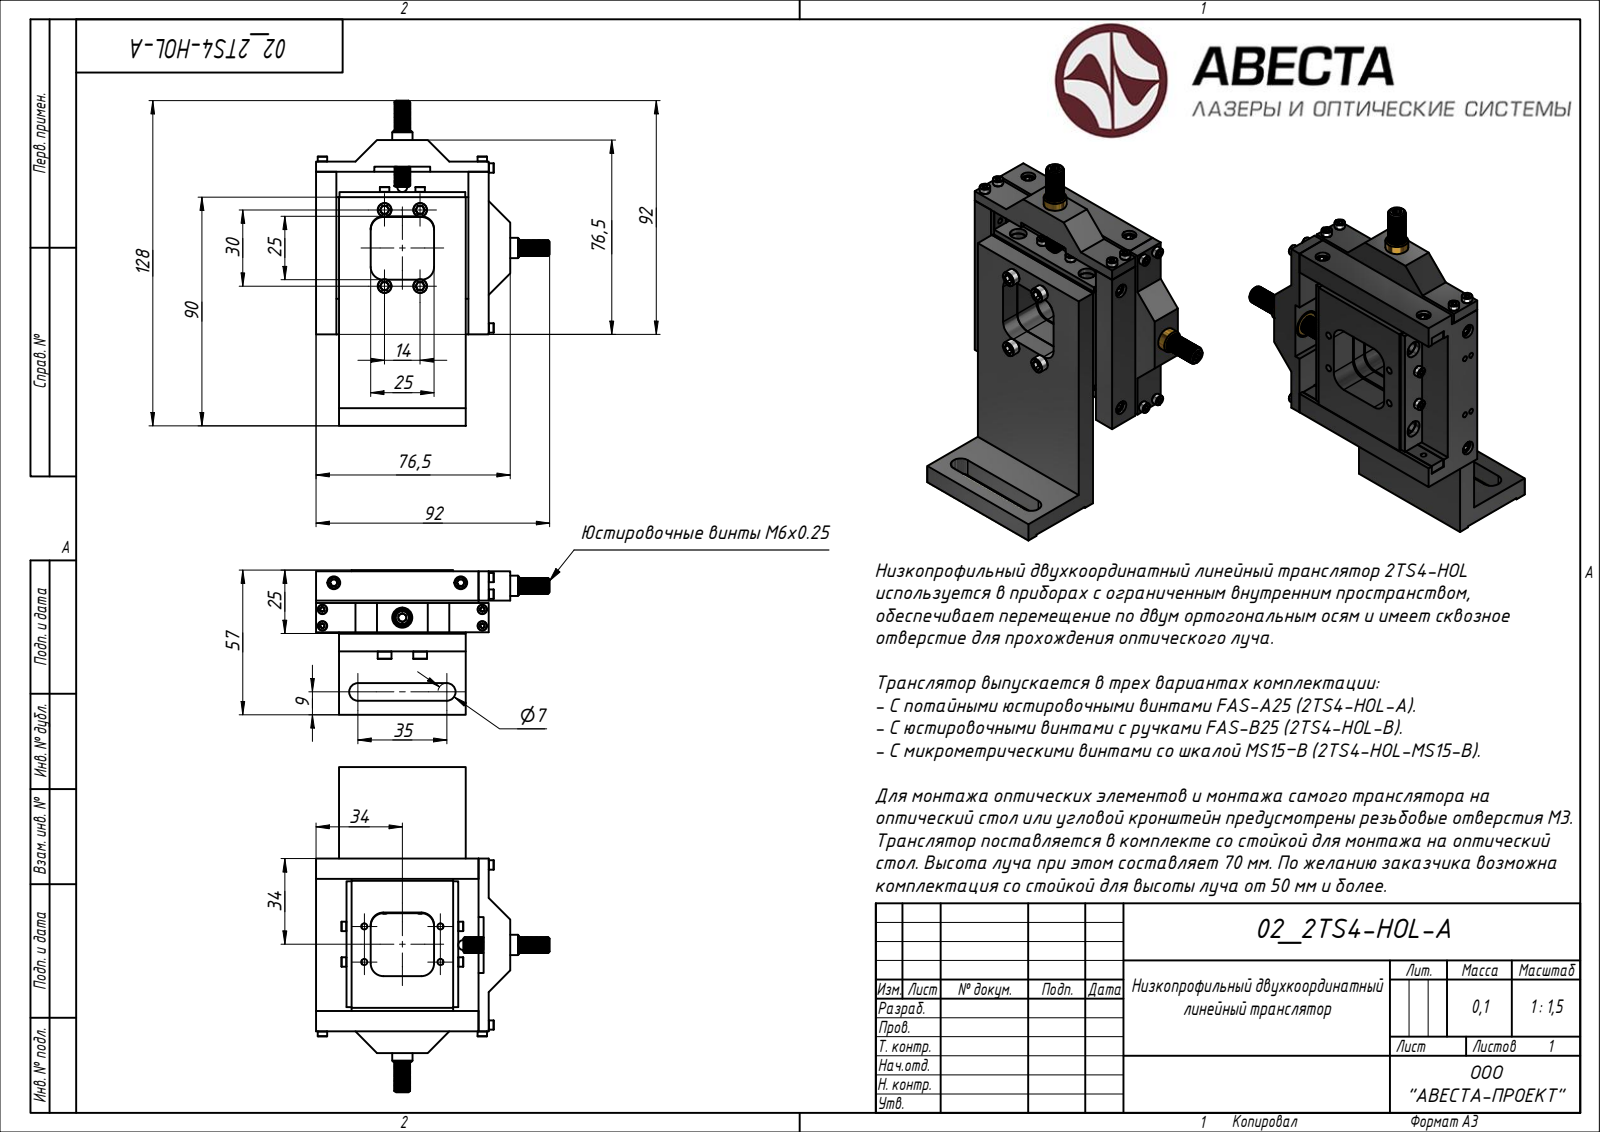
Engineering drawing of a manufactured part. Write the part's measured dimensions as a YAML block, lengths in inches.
step_written_by: "Rhino 7.34 (AUTOMOTIVE_DESIGN)"
units: inches
bodies: {solids: 16, faces: 1525, planar: 804, cylindrical: 538, other: 183}
overall_size: [5.039, 3.622, 2.244]
volume: 6.503
surface_area: 93.62
round_holes:
  - {diameter: 0.079, count: 9}
  - {diameter: 0.097, count: 6}
  - {diameter: 0.197, count: 4}
  - {diameter: 0.236, count: 4}
  - {diameter: 0.062, count: 2}
  - {diameter: 0.079, count: 2}
  - {diameter: 0.122, count: 2}
  - {diameter: 0.394, count: 2}
  - {diameter: 0.062, count: 1}
  - {diameter: 0.097, count: 1}
round_bosses_or_shafts:
  - {diameter: 0.118, count: 16}
  - {diameter: 0.146, count: 12}
  - {diameter: 0.079, count: 5}
  - {diameter: 0.213, count: 4}
  - {diameter: 0.177, count: 4}
  - {diameter: 0.354, count: 2}
  - {diameter: 0.315, count: 2}
  - {diameter: 0.236, count: 2}
partial_cylinders:
  - {radius: 0.118, count: 8}
  - {radius: 0.197, count: 8}
  - {radius: 0.031, count: 5}
  - {radius: 0.048, count: 5}
  - {radius: 0.048, count: 5}
  - {radius: 0.043, count: 4}
  - {radius: 0.031, count: 3}
  - {radius: 0.04, count: 3}
face_to_face_distances: [0.591, 0.374, 0.394, 0.354, 0.295, 0.197, 0.02, 0.276, 0.079, 0.315]
hole_center_spacings: [0.437, 0.593, 0.675, 0.764, 0.981, 1.247, 1.339, 1.379]
